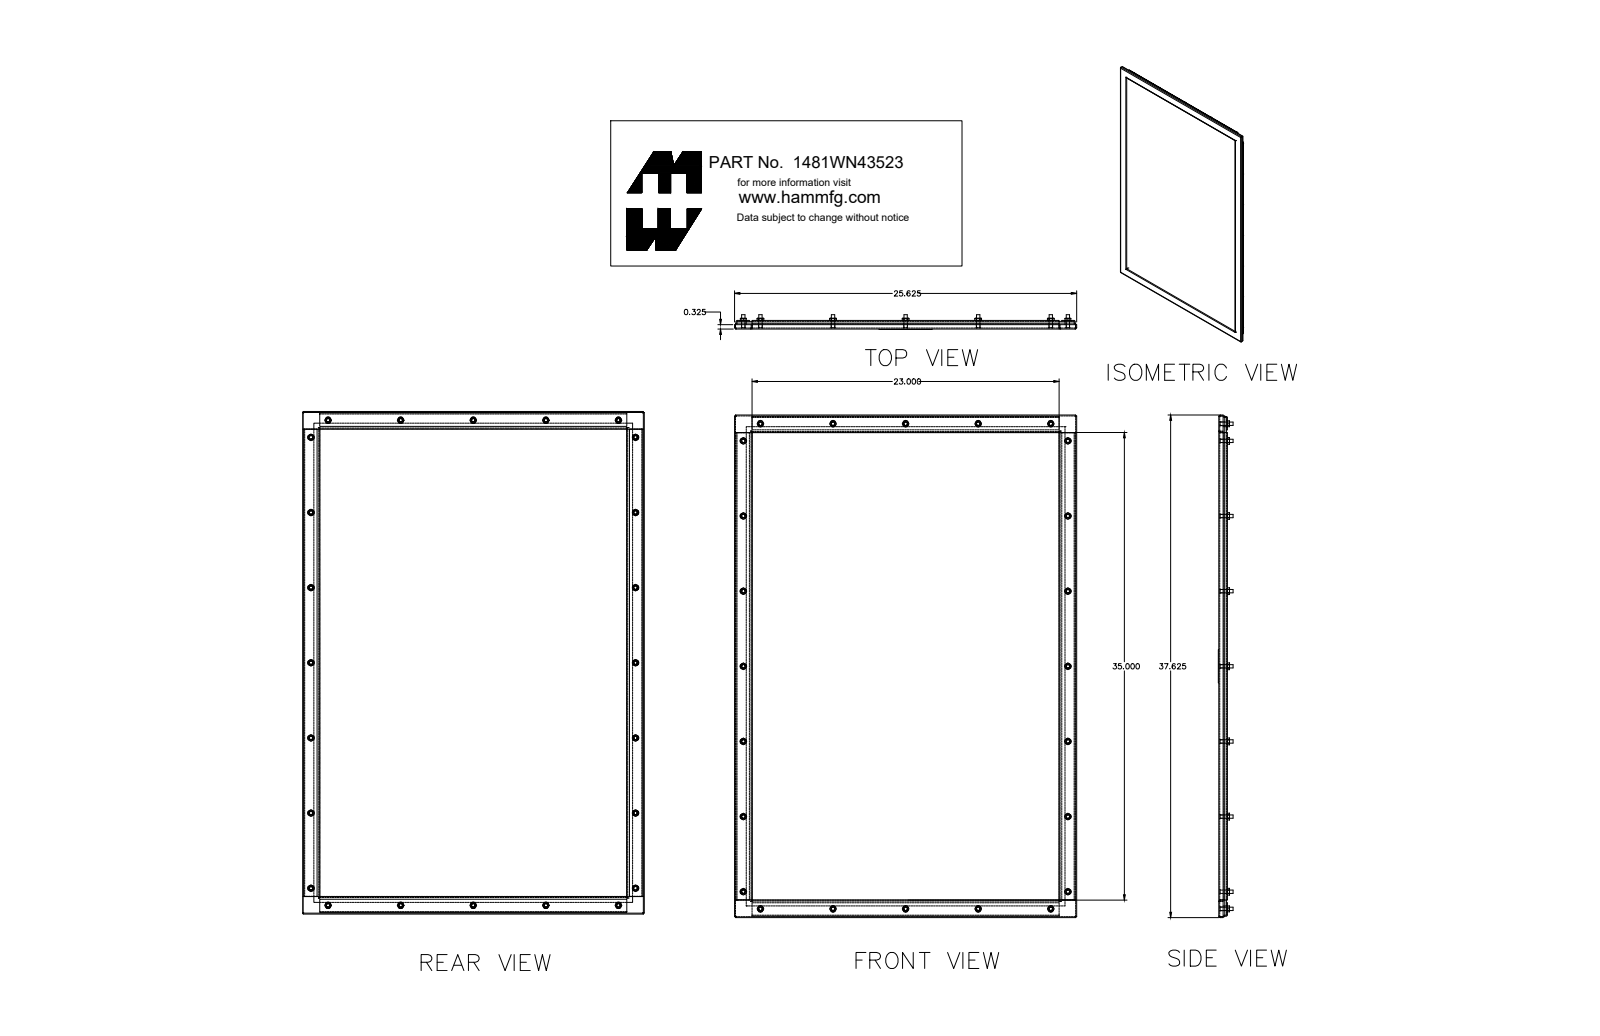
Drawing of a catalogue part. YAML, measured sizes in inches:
part_name: "1481WN43523_Default"
step_written_by: "SolidWorks 2019 (CONFIG_CONTROL_DESIGN)"
units: inches
bodies: {solids: 55, faces: 914, planar: 378, cylindrical: 216, other: 320}
overall_size: [38.025, 26.025, 1.072]
volume: 255.6
surface_area: 2941
round_holes:
  - {diameter: 0.25, count: 24}
  - {diameter: 0.328, count: 24}
round_bosses_or_shafts:
  - {diameter: 0.313, count: 24}
  - {diameter: 0.25, count: 22}
partial_cylinders:
  - {radius: 0.036, count: 8}
  - {radius: 0.108, count: 8}
  - {radius: 0.016, count: 4}
  - {radius: 0.088, count: 4}
face_to_face_distances: [0.25, 0.072, 0.253, 0.503, 0.325, 0.575, 0.575, 0.647, 0.322, 0.072]
hole_center_spacings: [24.955, 11.25, 24.313, 26.789, 5.625, 5.625, 22.5, 36.717]
